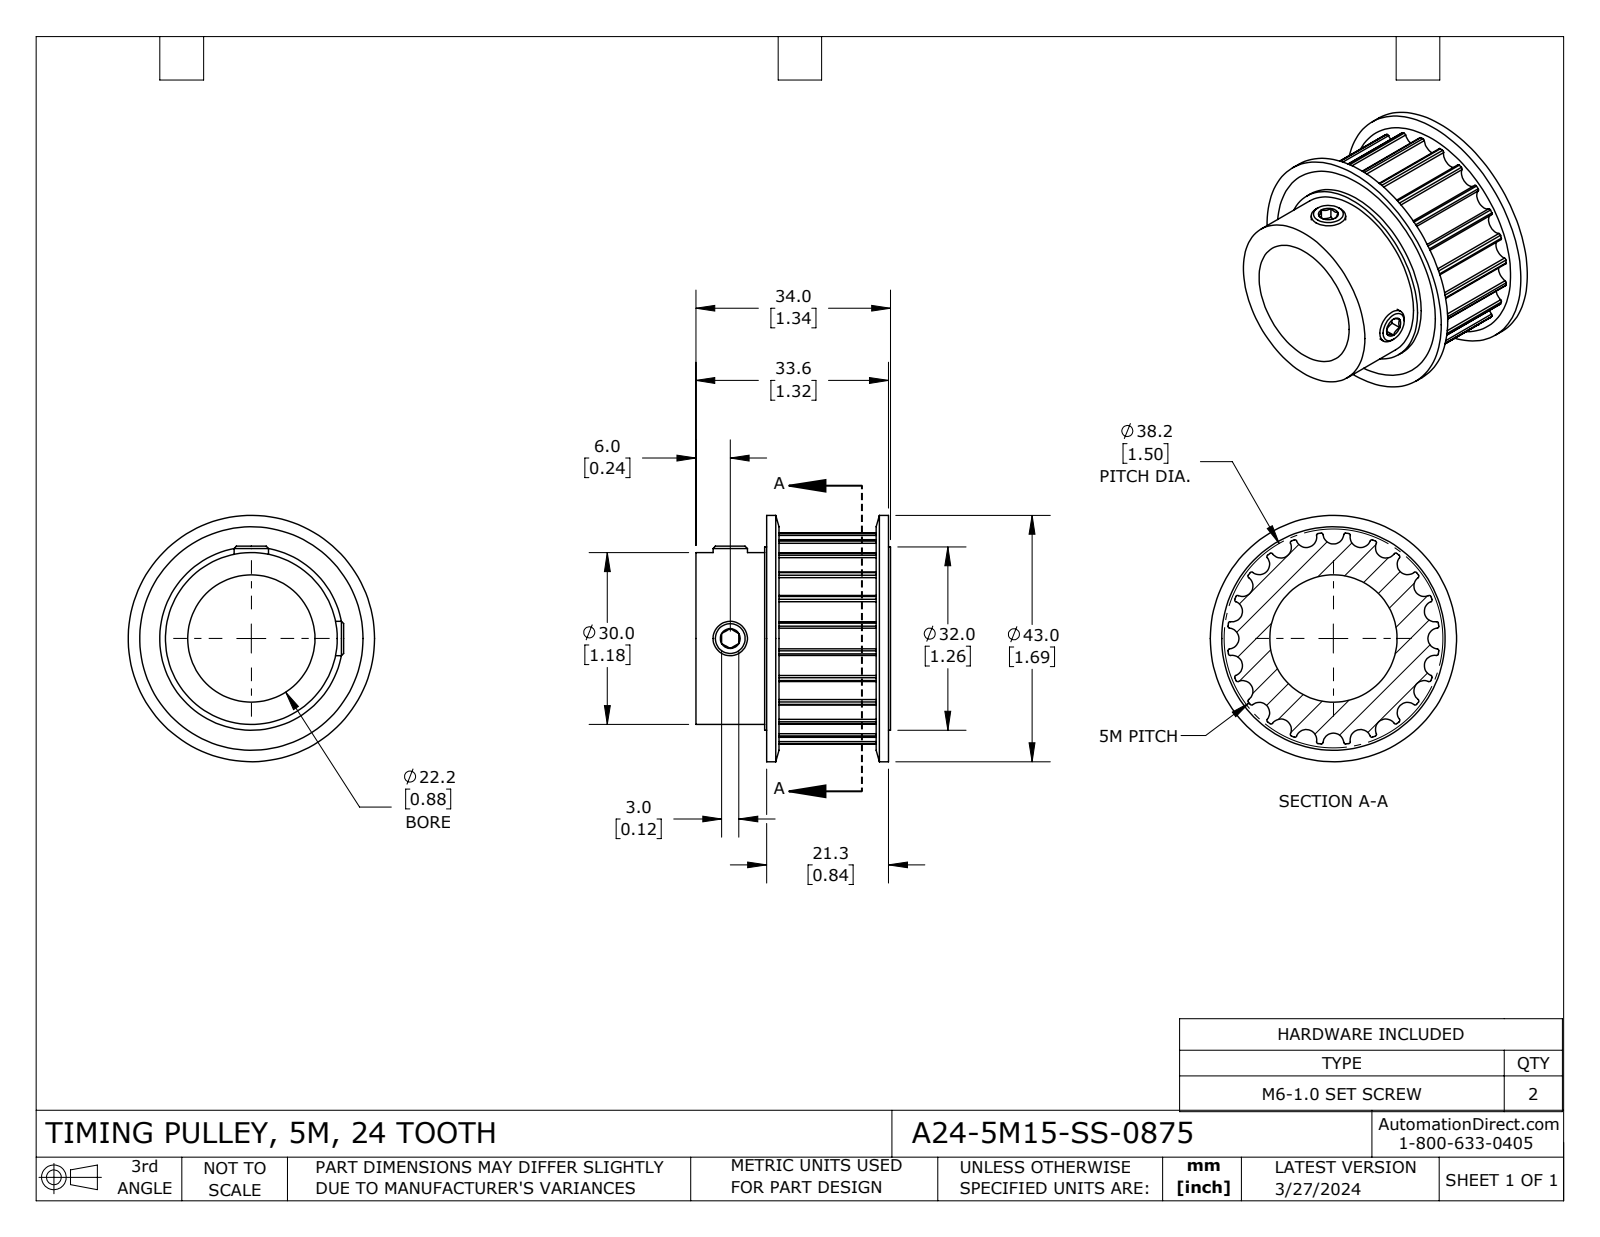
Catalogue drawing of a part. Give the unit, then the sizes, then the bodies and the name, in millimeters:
Units: millimetres
Overall size (bounding box): 43 × 43 × 34
Round holes (diameter × count): ⌀5 ×2, ⌀22.23 ×1, ⌀32 ×1
Round bosses / shafts (diameter × count): ⌀6 ×2, ⌀43 ×1, ⌀30 ×1
Partial cylindrical surfaces — rounded edges, fillets, slot ends (radius × count): R0.3 ×48, R1.82 ×24, R18.52 ×1
Main face-to-face distances: 1.6, 18.6, 17, 2.5, 19.5, 0.9, 21.1, 20.2, 34, 33.1
Volume: 17 396 mm³ · Surface area: 11 632 mm²
Bodies: 5 solids, 202 faces (25 planar, 143 cylindrical, 34 other)
Part name (STEP PRODUCT): A24-5M15-SS-0875
STEP written by: SolidWorks 2021 (CONFIG_CONTROL_DESIGN)
